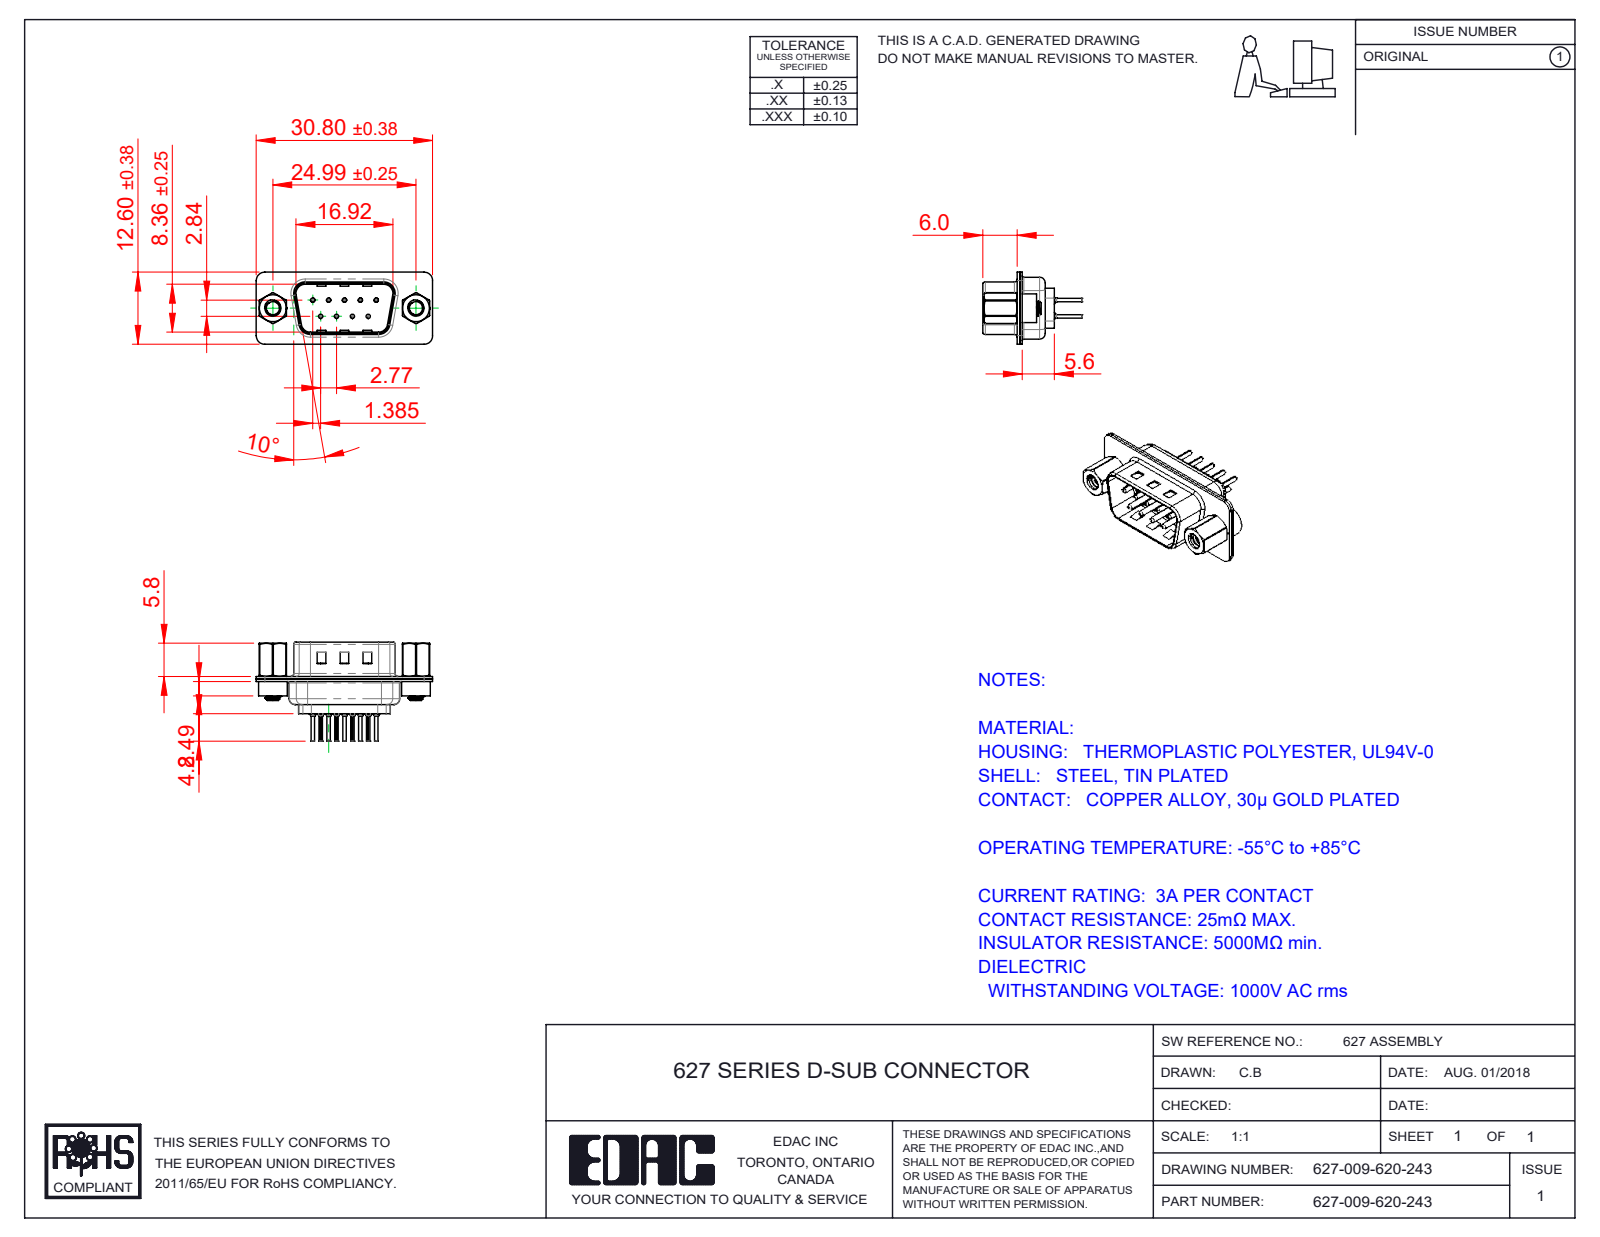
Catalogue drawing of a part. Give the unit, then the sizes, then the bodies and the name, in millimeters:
Units: millimetres
Overall size (bounding box): 30.8 × 17.3 × 12.6
Round holes (diameter × count): ⌀0.2 ×9, ⌀0.35 ×9, ⌀1.1 ×9, ⌀1.6 ×9, ⌀2.26 ×2, ⌀2.29 ×2, ⌀4 ×2, ⌀4.8 ×2
Round bosses / shafts (diameter × count): ⌀2 ×9, ⌀1.5 ×9, ⌀0.75 ×9, ⌀0.6 ×9, ⌀5 ×2, ⌀4.9 ×2, ⌀2.79 ×2
Partial cylindrical surfaces — rounded edges, fillets, slot ends (radius × count): R0.1 ×18, R1.5 ×18, R2 ×12, R0.5 ×8, R1.6 ×8, R0.25 ×4, R0.6 ×4, R0.65 ×4
Main face-to-face distances: 0.45, 0.4, 0.9, 0.82, 9.58, 1.4, 8.76, 0.5, 1.5, 5.6
Hole centre spacings: 3.16, 2.77, 5.54, 5.03, 5.04, 8.31, 7.48, 7.49
Volume: 1 519 mm³ · Surface area: 4 406 mm²
Bodies: 16 solids, 1308 faces (345 planar, 532 cylindrical, 431 other)
Part name (STEP PRODUCT): 627 Contact Row 2_20L; 627 Housing_09 LP; 627-009-620-043; 627 Contact Row 1_20L (+4 more)
STEP written by: SolidWorks 2020 (CONFIG_CONTROL_DESIGN)
